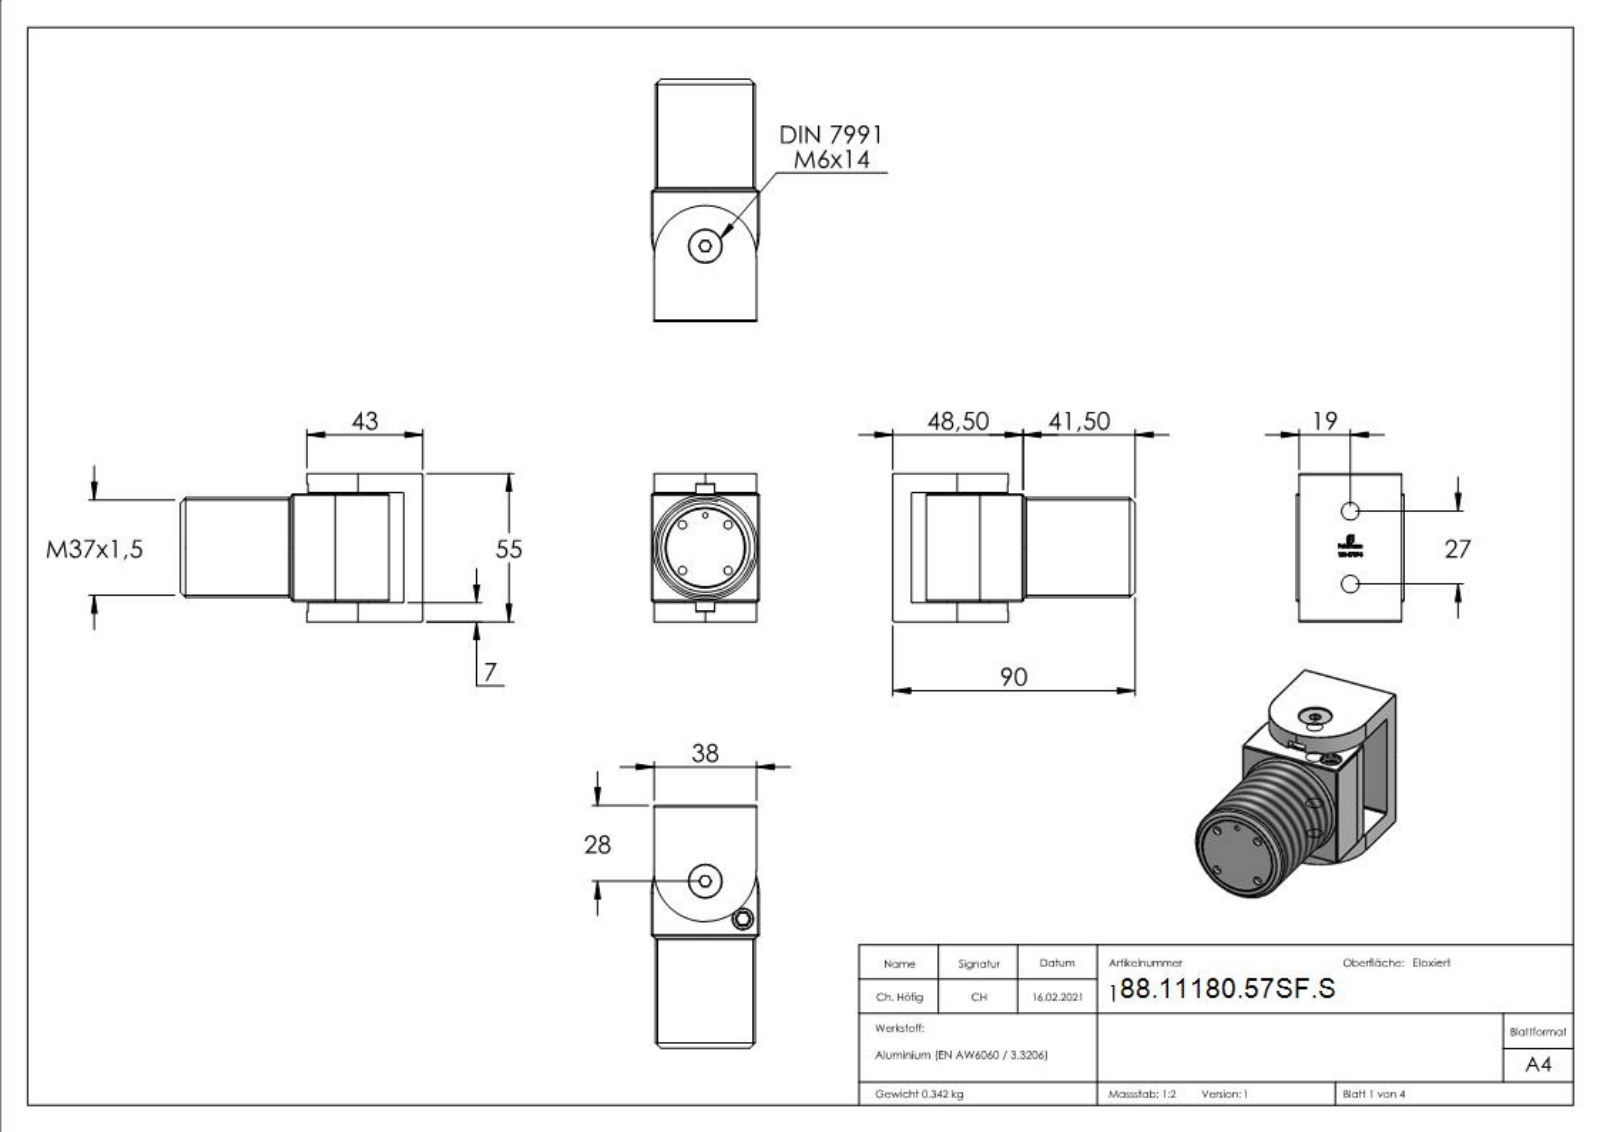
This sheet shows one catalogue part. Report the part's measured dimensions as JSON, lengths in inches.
{"part_name": "DIN-7991 M3-M10; DIN-7991 M3-M10_DIN7991 M6x14; Teil2; Teil2_180-57SF-S Teil2 (+3 more)", "step_written_by": "SolidWorks 2018 (CONFIG_CONTROL_DESIGN)", "units": "inches", "bodies": {"solids": 5, "faces": 519, "planar": 231, "cylindrical": 88, "other": 200}, "overall_size": [551.199, 236.22, 236.22], "volume_in3": 7.625, "surface_area_in2": 41.57, "round_holes": [[0.122, 4], [0.256, 3], [0.492, 3], [0.075, 1], [0.197, 1], [0.315, 1], [0.618, 1], [0.945, 1], [1.169, 1]], "round_bosses_or_shafts": [[1.457, 1], [1.161, 1], [1.024, 1], [0.929, 1], [0.61, 1], [0.472, 1], [0.307, 1], [0.236, 1]], "partial_cylinders_radius": [[0.02, 12], [0.748, 1], [0.787, 1]], "face_to_face_distances": [0.276, 1.89, 1.87, 0.02, 0.295, 1.594, 2.165, 1.575, 0.039, 1.535], "hole_center_spacings": [0.388, 0.473, 0.669, 0.928, 0.362, 0.531, 0.873, 0.945]}
